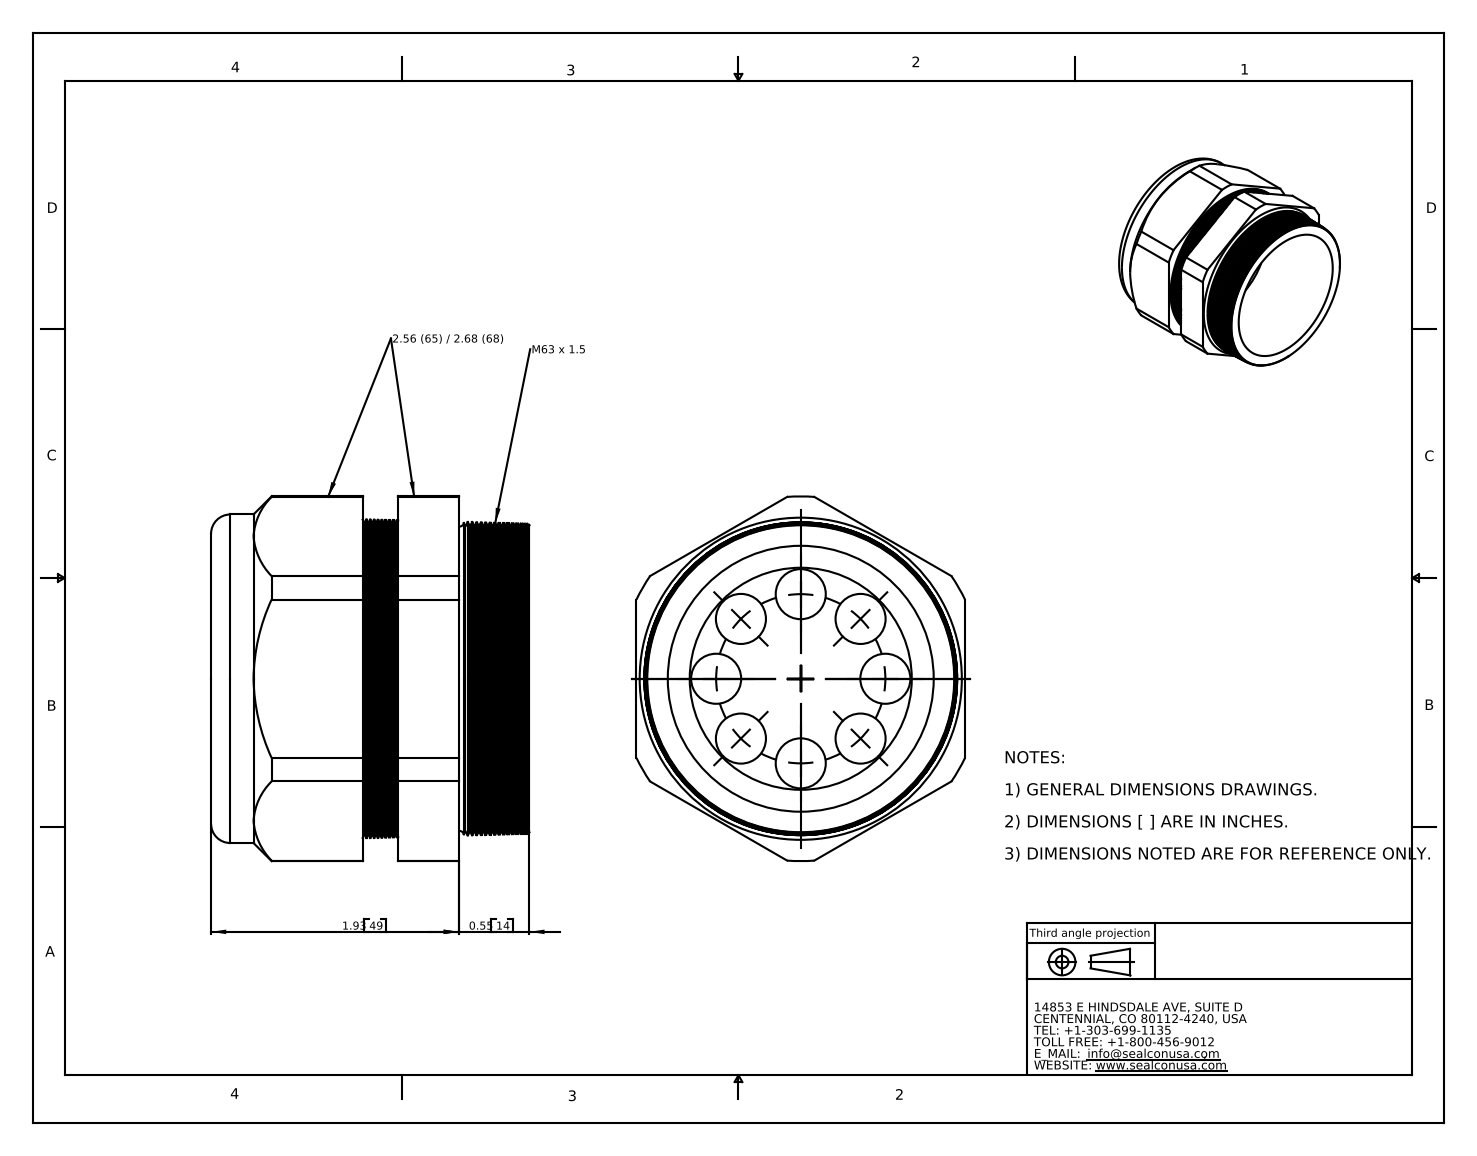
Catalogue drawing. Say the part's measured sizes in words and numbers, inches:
The part is named "CD63M1-GY". Its 3-D file was written by "SolidWorks 2007 (CONFIG_CONTROL_DESIGN)". It is 2 solids with 214 faces: 20 planar, 36 cylindrical and 158 other. Overall it measures 2.842 by 2.56 by 2.48 inches. Its volume is 7.094 cubic inches and its surface area 56.43 square inches. Round holes: 8 of diameter 0.39, 1 of diameter 1.71, 1 of diameter 1.73. Round bosses or shafts: 1 of diameter 2.56. Partial cylindrical surfaces (rounded edges, fillets, slot ends): 1 of radius 1.421. The main face-to-face distances are 2.56, 0.5, 0.02, 0.48, 2.48, 2.46, 1.98, 1.458, 1.438, 0.958. The hole center spacings are 0.504, 0.659, 1.218, 0.932, 0.932, 1.318, 1.319.
